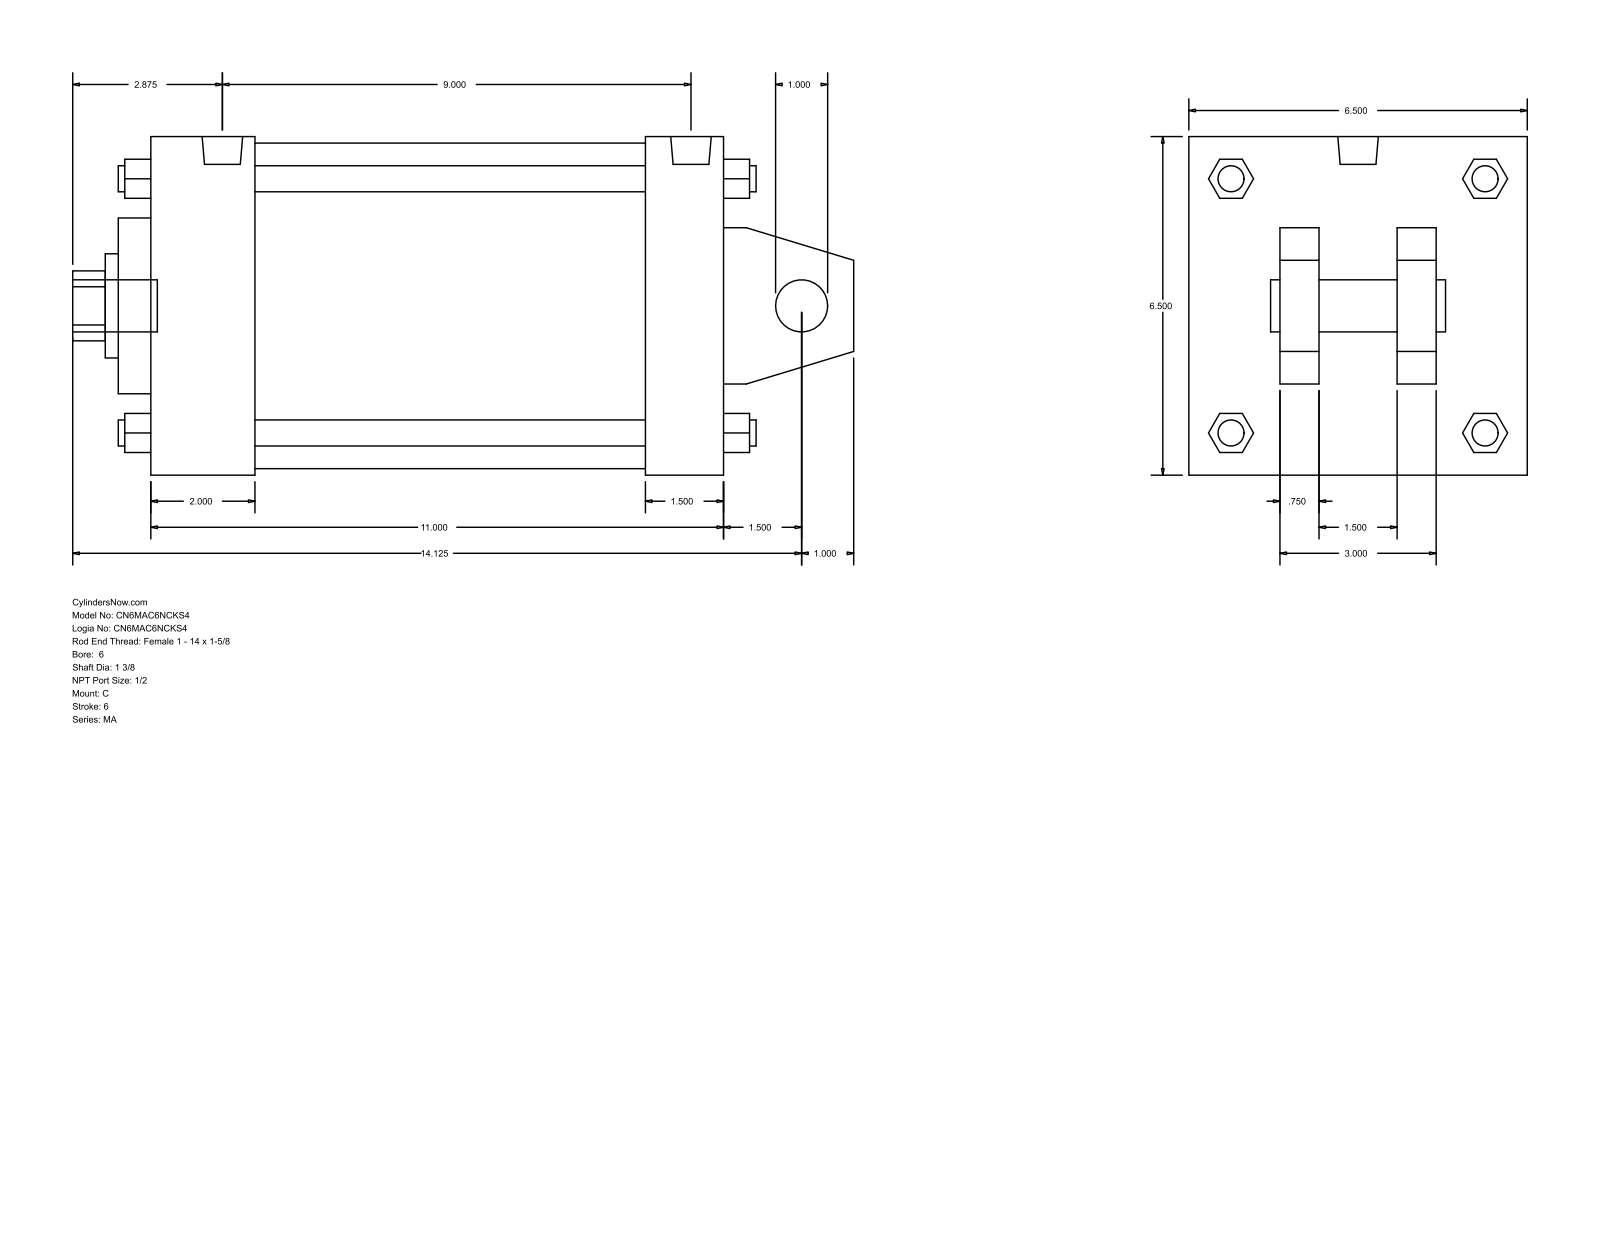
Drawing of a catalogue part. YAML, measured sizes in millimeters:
part_name: "MA_C__0600_1.375"
step_written_by: "GSSL Pune (CONFIG_CONTROL_DESIGN)"
units: millimeters
bodies: {solids: 0, faces: 141, planar: 109, cylindrical: 32, other: 0}
overall_size: [381, 165.1, 165.1]
round_holes:
  - {diameter: 25.4, count: 1}
  - {diameter: 34.92, count: 1}
  - {diameter: 50.8, count: 1}
  - {diameter: 85.72, count: 1}
  - {diameter: 158.75, count: 1}
round_bosses_or_shafts:
  - {diameter: 17.46, count: 4}
  - {diameter: 12.7, count: 4}
  - {diameter: 19.77, count: 2}
  - {diameter: 25.4, count: 1}
partial_cylinders:
  - {radius: 17.06, count: 1}
face_to_face_distances: [165.1, 279.4, 38.1, 19.05, 63.5, 101.6, 50.8, 120.65, 44.45, 241.3]
